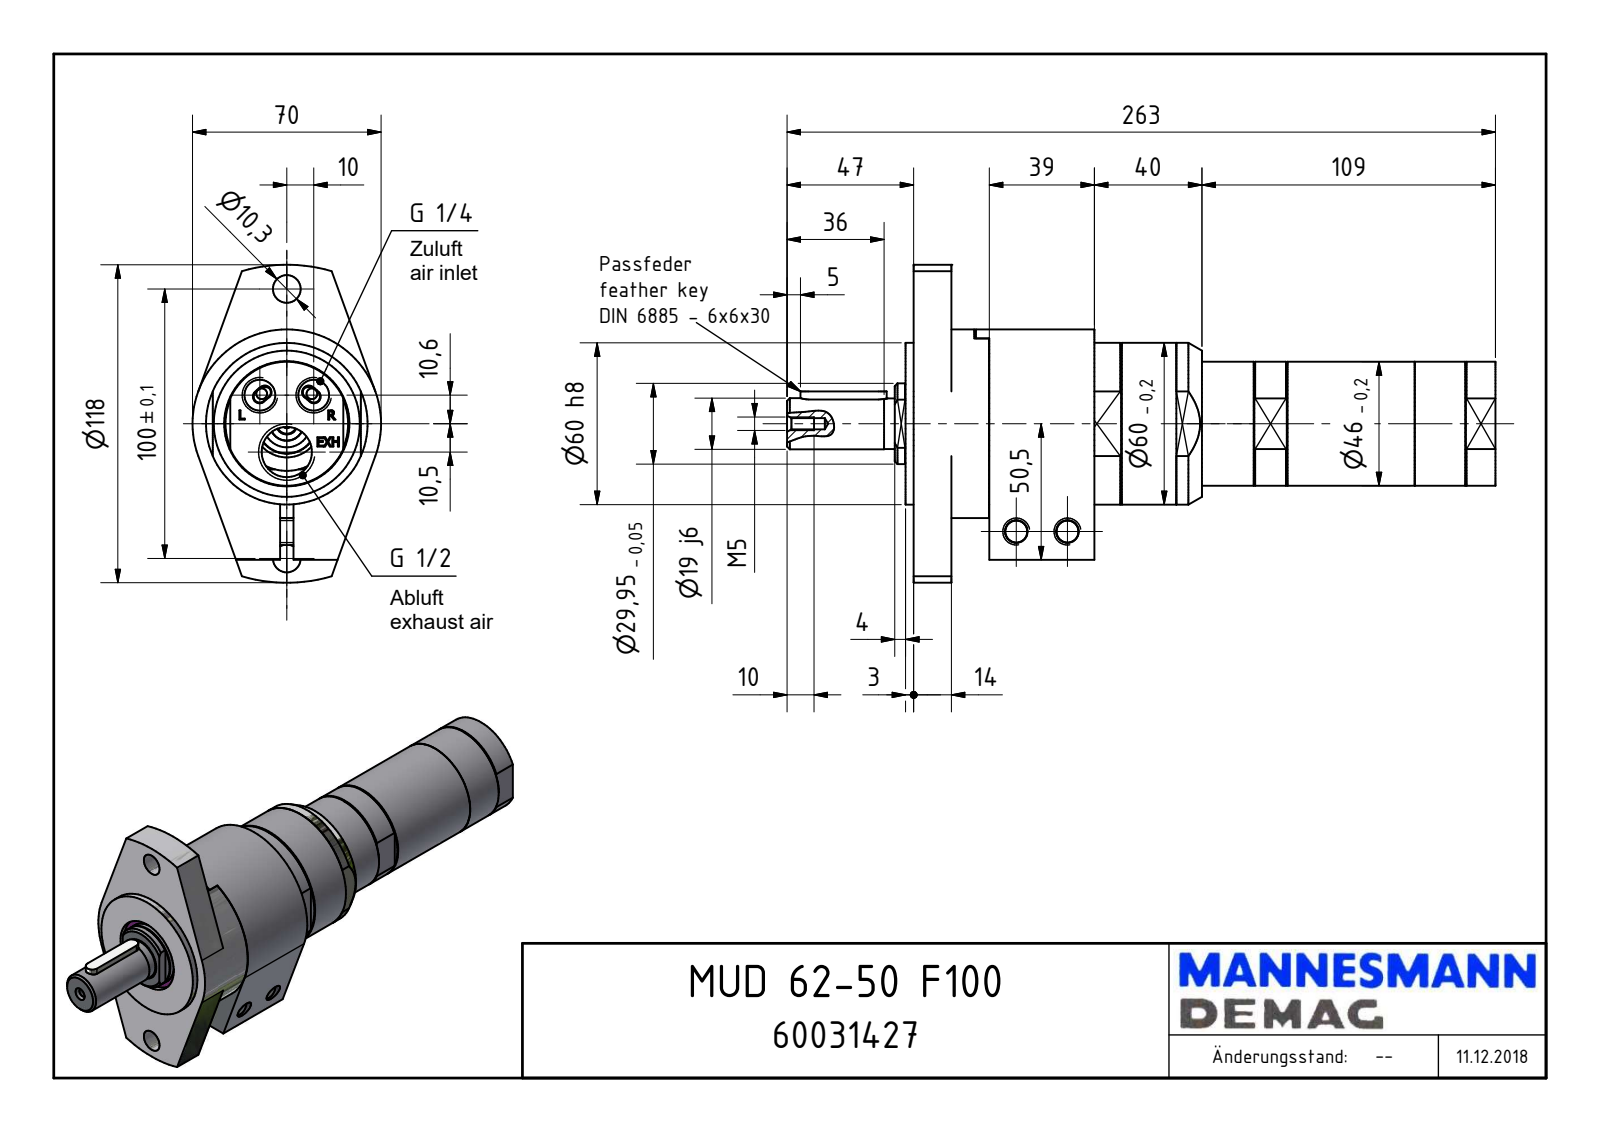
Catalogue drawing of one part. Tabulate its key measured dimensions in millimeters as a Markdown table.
| quantity | value |
| --- | --- |
| part name | MUD 62-50 F100_60031427 |
| STEP written by | Autodesk Inventor 2018 (AUTOMOTIVE_DESIGN) |
| units | millimeters |
| bodies | 1 solid, 282 faces (158 planar, 66 cylindrical, 58 other) |
| overall size | 263 × 118 × 70 |
| volume | 619 173 mm³ |
| surface area | 76 903 mm² |
| round holes (diameter × count) | 8.38 × 2, 10.3 × 2, 10.5 × 2, 11.45 × 2, 18 × 2, 1.55 × 1, 4 × 1, 4.13 × 1, 5.5 × 1, 18.63 × 1, 35 × 1, 36.5 × 1 |
| round bosses / shafts (diameter × count) | 16 × 2, 10 × 2, 70 × 1, 60 × 1, 55.18 × 1, 46 × 1, 40 × 1, 33.83 × 1 |
| partial cylindrical surfaces (radius × count) | 3 × 2, 5 × 2, 19 × 1, 25.37 × 1, 59 × 1 |
| main face-to-face distances | 14, 17, 3, 70.1, 67.1, 53.1, 6.5, 31.1, 28.1, 14.1 |
| hole center spacings | 14.57, 23.35, 40.65, 50, 61.42, 10.5, 19, 20 |
